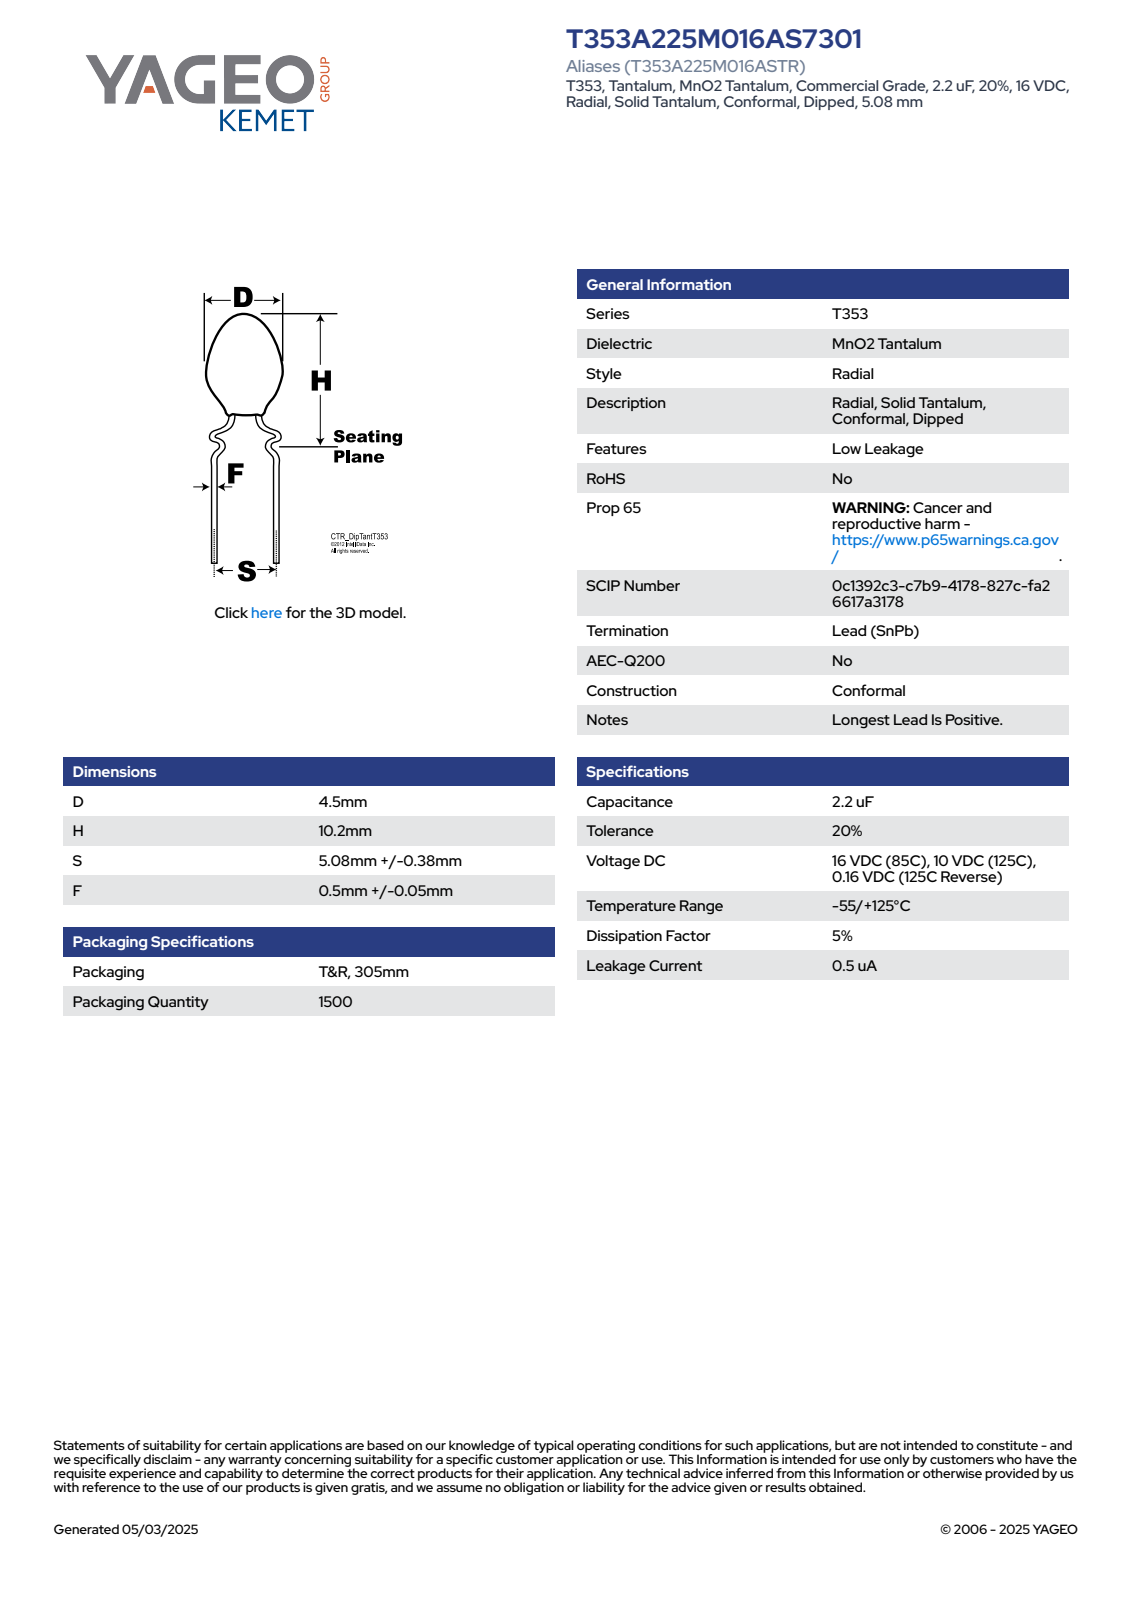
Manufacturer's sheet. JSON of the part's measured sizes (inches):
{"part_name": "CTR_T353_D4.5H10.2S5.08LL5.56F0.55", "step_written_by": "SolidWorks 2014 (AUTOMOTIVE_DESIGN)", "units": "inches", "bodies": {"solids": 1, "faces": 89, "planar": 29, "cylindrical": 10, "other": 50}, "overall_size": [0.62, 0.222, 0.177], "volume_in3": 0.007, "surface_area_in2": 0.233, "round_bosses_or_shafts": [[0.022, 2], [0.177, 1]], "partial_cylinders_radius": [[0.088, 1]], "face_to_face_distances": [0.276, 0.345, 0.62, 0.504, 0.159, 0.116, 0.472, 0.128, 0.032, 0.148]}
